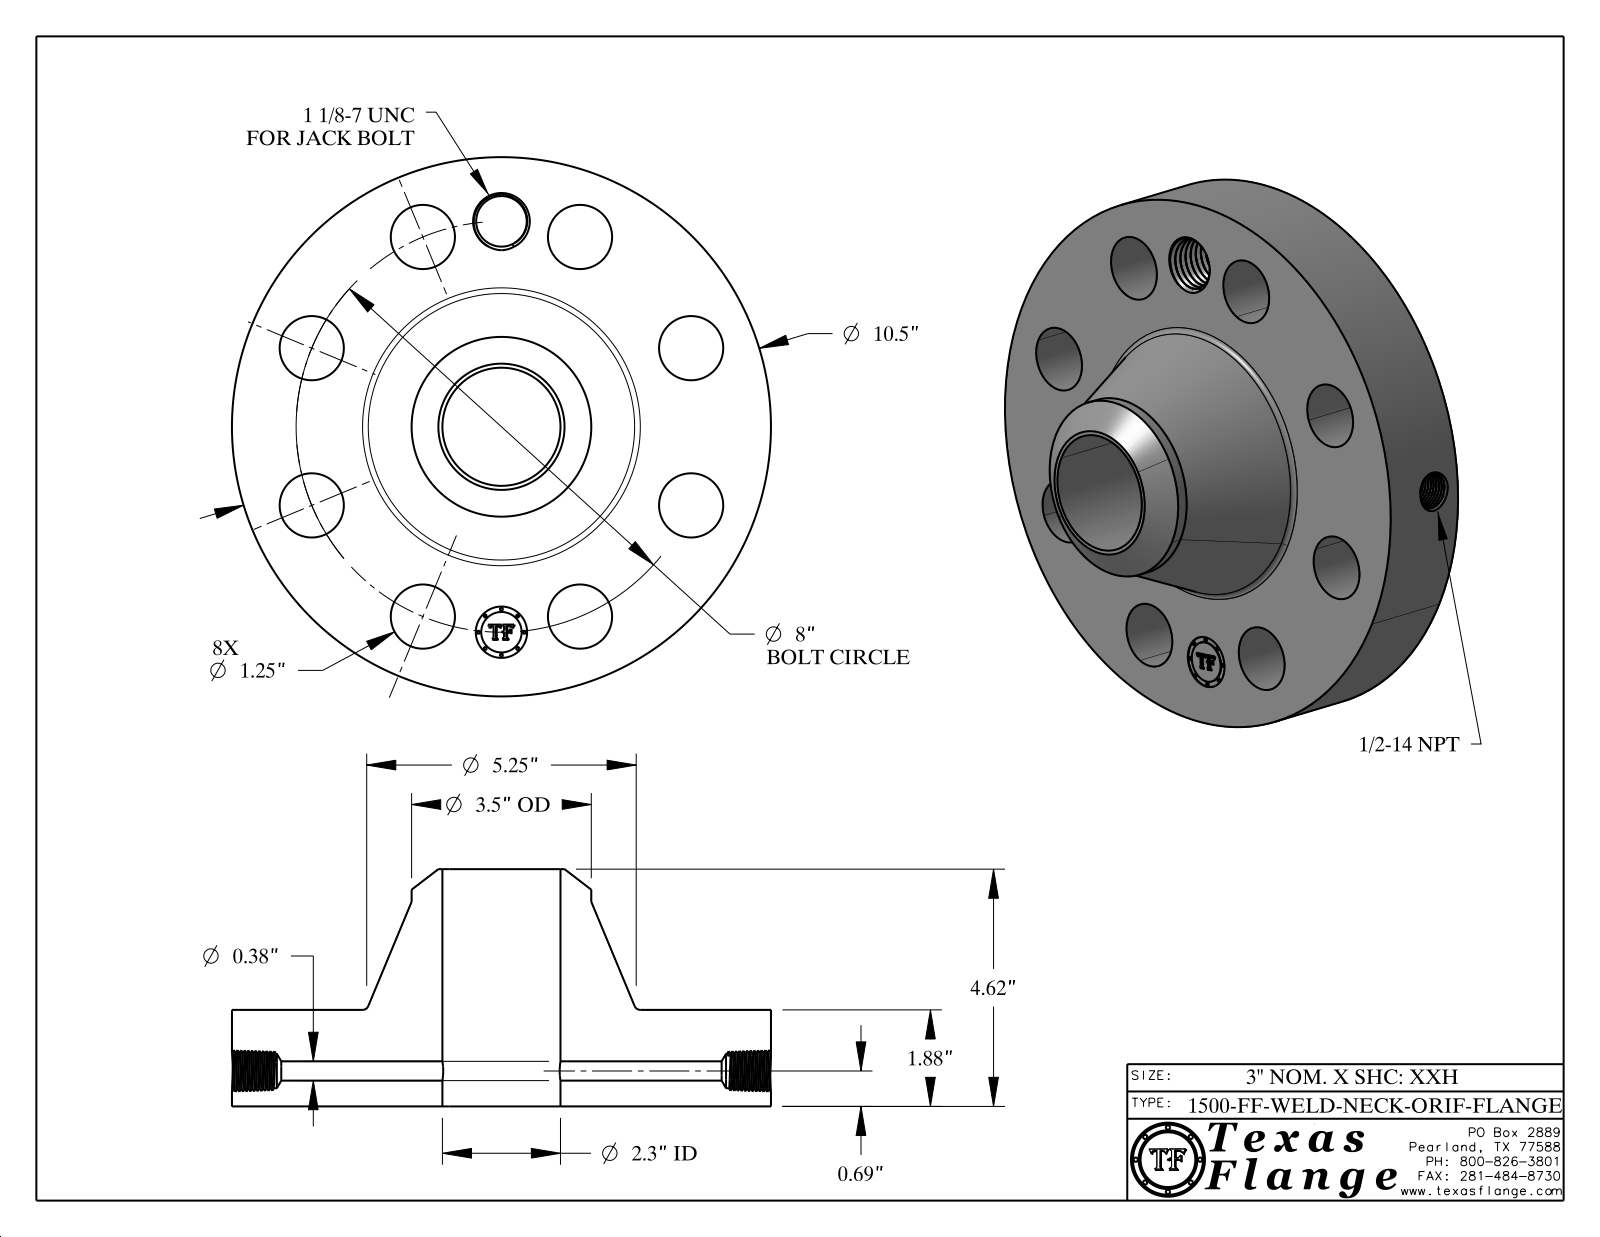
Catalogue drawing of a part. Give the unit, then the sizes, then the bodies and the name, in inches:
Units: inches
Overall size (bounding box): 10.5 × 10.5 × 4.62
Round holes (diameter × count): ⌀1.25 ×8, ⌀0.375 ×1, ⌀0.672 ×1, ⌀0.984 ×1, ⌀1 ×1, ⌀2.3 ×1
Round bosses / shafts (diameter × count): ⌀0.061 ×8, ⌀10.5 ×1, ⌀3.5 ×1, ⌀0.788 ×1
Main face-to-face distances: 1.88, 4.62, 2.74, 1.865, 0.015, 2.755, 0.298, 0.293, 0.054, 0.248
Hole centre spacings: 4, 5.657, 7.391, 1.561, 3.061, 3.062, 4.445, 6.652
Volume: 159.2 in³ · Surface area: 343.7 in²
Bodies: 1 solid, 757 faces (368 planar, 88 cylindrical, 301 other)
Part name (STEP PRODUCT): 1500-FF-WELD-NECK
STEP written by: CATIA V5 STEP AP214 (AUTOMOTIVE_DESIGN)
